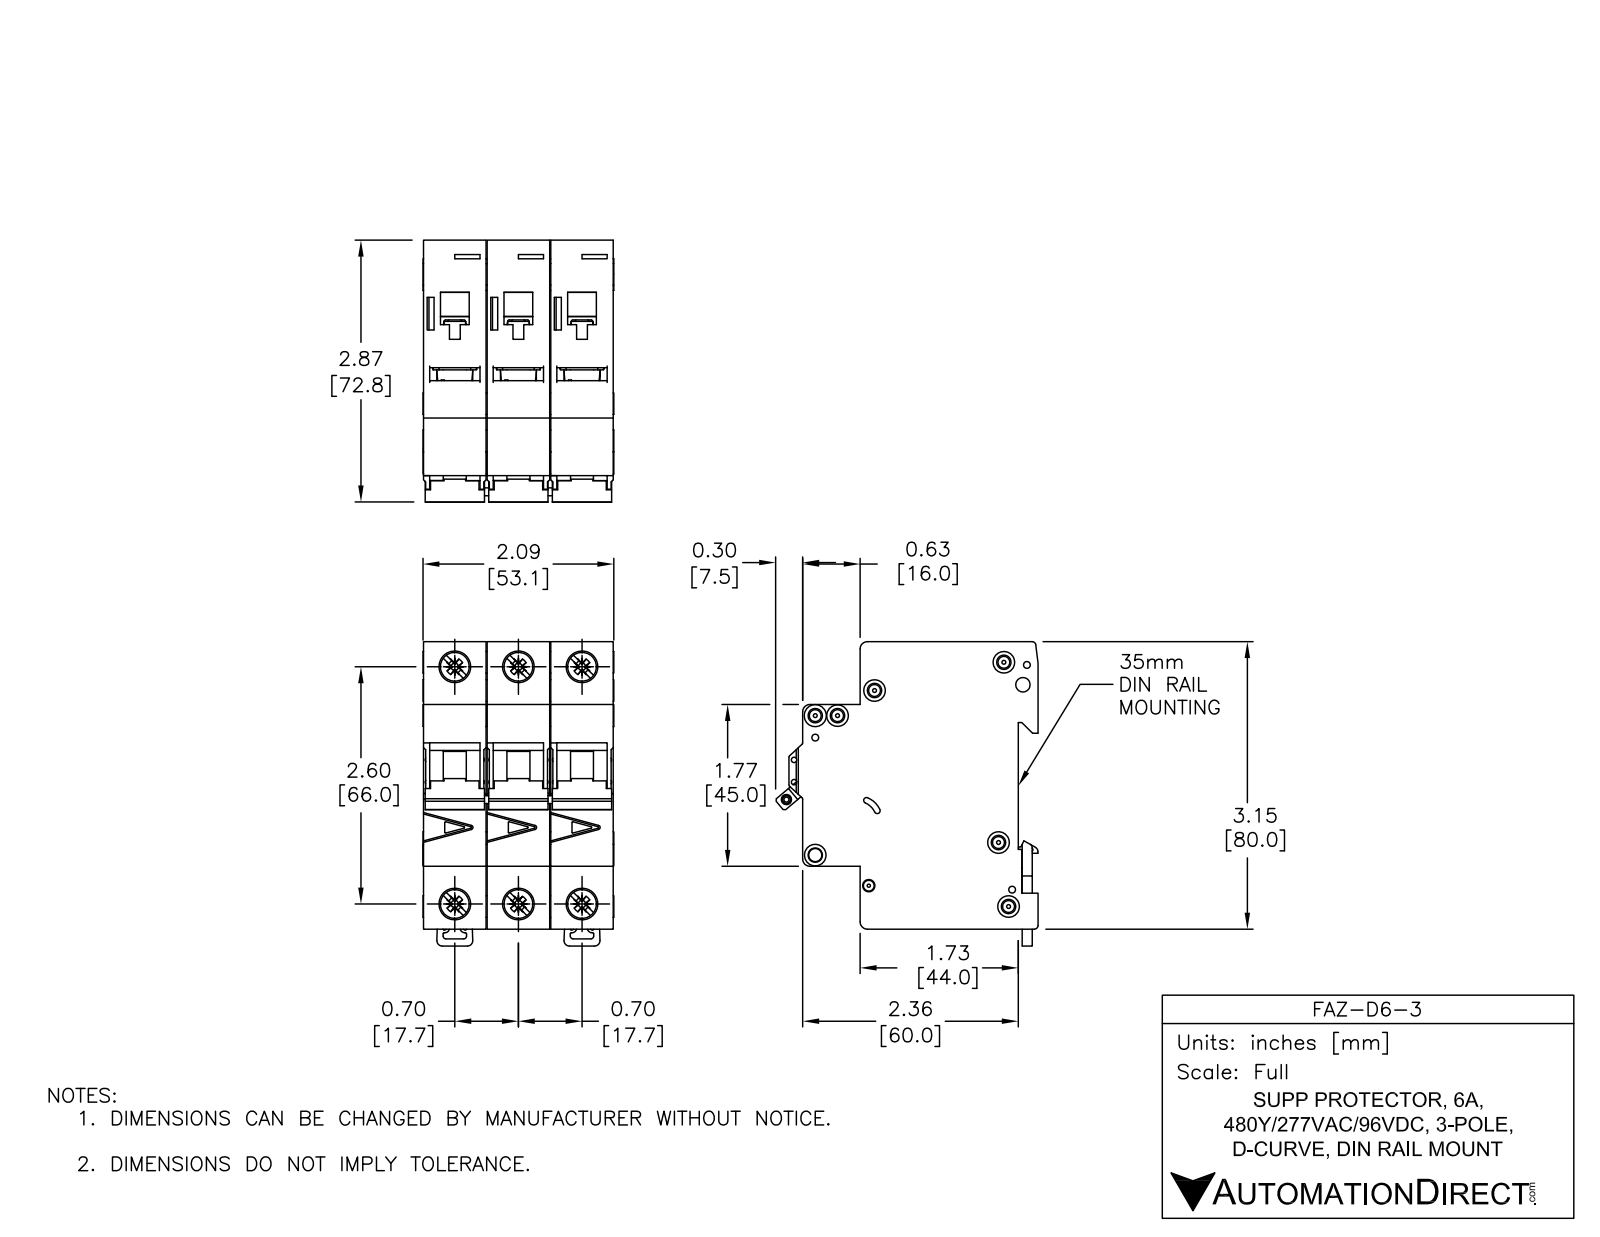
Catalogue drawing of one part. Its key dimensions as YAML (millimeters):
part_name: "FAZ-D6-3"
step_written_by: "SolidWorks 2014 (AUTOMOTIVE_DESIGN)"
units: millimeters
bodies: {solids: 11, faces: 1650, planar: 697, cylindrical: 590, other: 363}
overall_size: [84.78, 73.04, 53.1]
volume: 224680
surface_area: 58052
round_holes:
  - {diameter: 3.6, count: 6}
  - {diameter: 8.2, count: 4}
  - {diameter: 1.9, count: 3}
  - {diameter: 1.09, count: 2}
  - {diameter: 1.5, count: 2}
  - {diameter: 4, count: 2}
  - {diameter: 7.15, count: 2}
  - {diameter: 2.15, count: 1}
  - {diameter: 2.2, count: 1}
  - {diameter: 2.55, count: 1}
  - {diameter: 3.3, count: 1}
  - {diameter: 3.4, count: 1}
round_bosses_or_shafts:
  - {diameter: 6, count: 4}
  - {diameter: 2.5, count: 3}
  - {diameter: 8.2, count: 2}
partial_cylinders:
  - {radius: 0.25, count: 68}
  - {radius: 0.5, count: 25}
  - {radius: 1, count: 12}
  - {radius: 2, count: 12}
  - {radius: 0.2, count: 11}
  - {radius: 1.8, count: 3}
  - {radius: 0.8, count: 2}
  - {radius: 3, count: 2}
face_to_face_distances: [17.7, 17.5, 35.4, 35.2, 52.9, 17.9, 79.48, 5.5, 49.5, 44]
hole_center_spacings: [17.7, 68.33, 66, 6.2, 13.64, 35.4, 74.89, 4.81]
